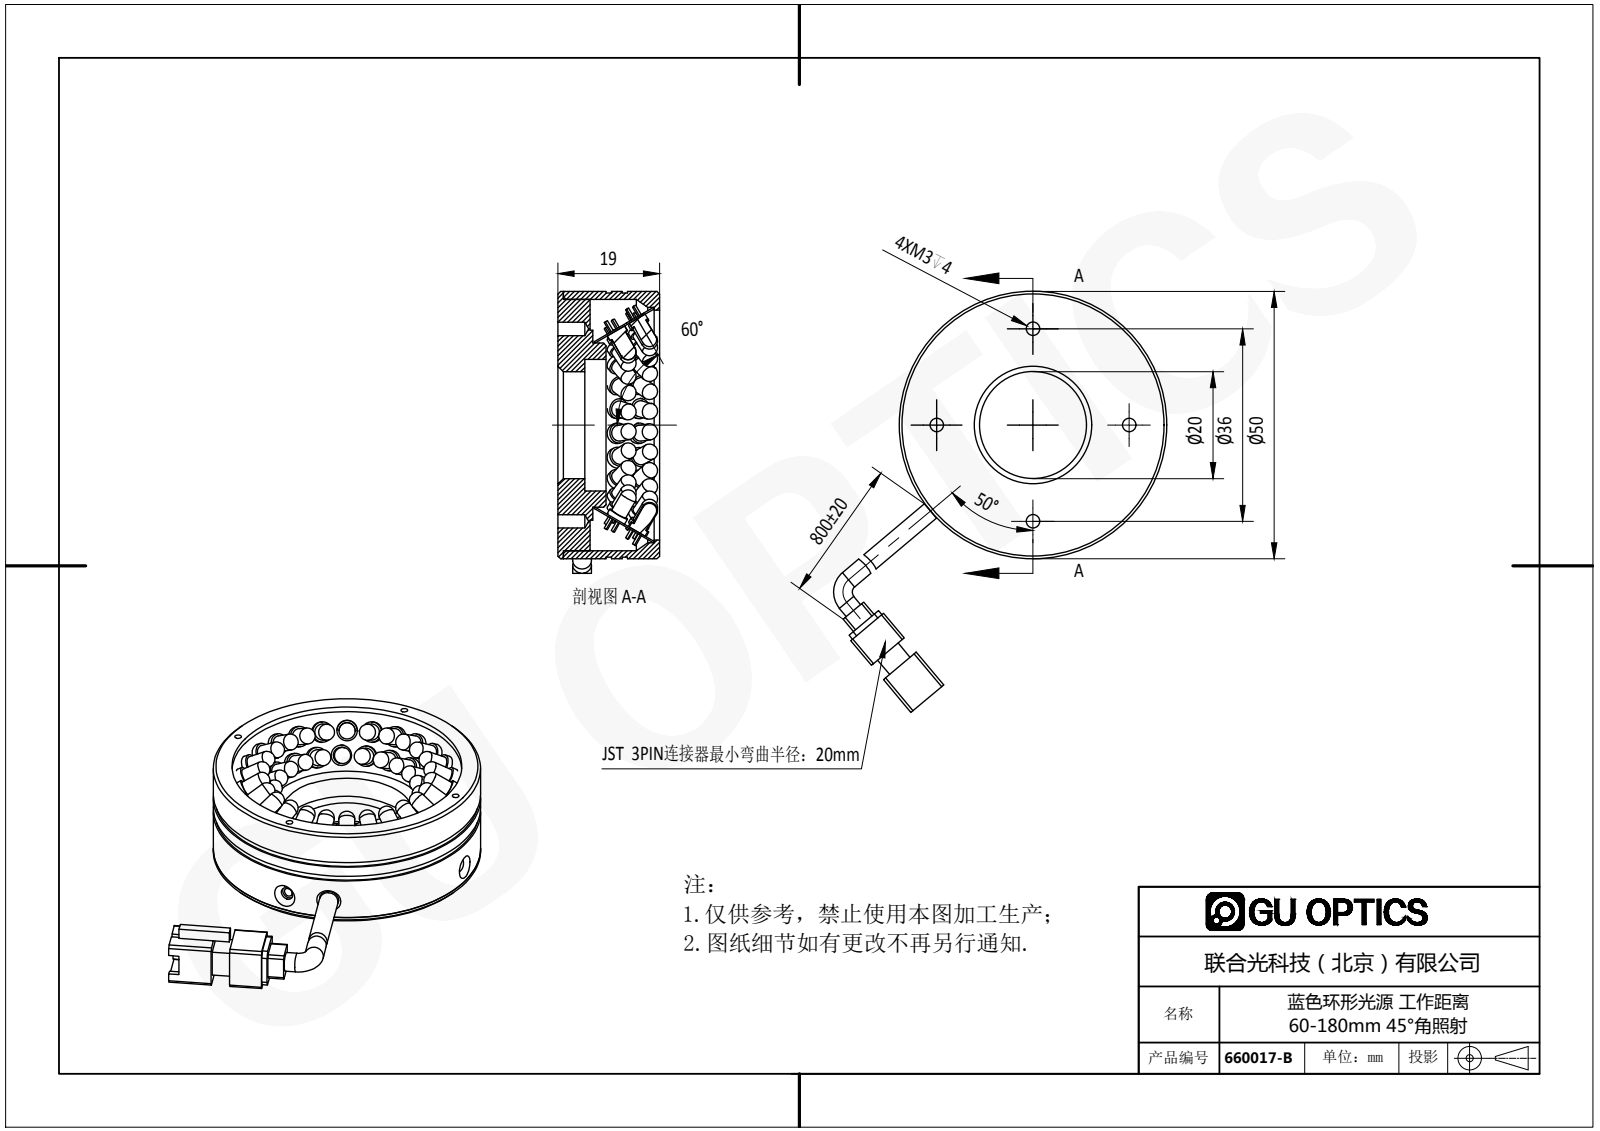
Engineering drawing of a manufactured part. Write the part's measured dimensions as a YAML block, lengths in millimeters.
part_name: "660017-B"
step_written_by: "SolidWorks 2016 (AUTOMOTIVE_DESIGN)"
units: millimeters
bodies: {solids: 54, faces: 1066, planar: 662, cylindrical: 300, other: 104}
overall_size: [82.93, 50, 19]
volume: 17639
surface_area: 20260
round_holes:
  - {diameter: 1.25, count: 4}
  - {diameter: 2.5, count: 4}
  - {diameter: 1.6, count: 2}
  - {diameter: 2.4, count: 2}
  - {diameter: 3, count: 2}
  - {diameter: 3.6, count: 1}
  - {diameter: 20, count: 1}
  - {diameter: 24.6, count: 1}
  - {diameter: 43, count: 1}
  - {diameter: 44, count: 1}
round_bosses_or_shafts:
  - {diameter: 3.8, count: 49}
  - {diameter: 3, count: 47}
  - {diameter: 3.5, count: 2}
  - {diameter: 50, count: 1}
  - {diameter: 49.4, count: 1}
  - {diameter: 47, count: 1}
  - {diameter: 35.54, count: 1}
  - {diameter: 30.72, count: 1}
partial_cylinders:
  - {radius: 0.5, count: 12}
  - {radius: 1, count: 4}
  - {radius: 4, count: 1}
face_to_face_distances: [1, 6, 0.5, 5, 5.5, 8, 3, 13, 2.5, 1.5]
hole_center_spacings: [11.66, 20.95, 23, 32.53, 18, 25.46, 35.6, 39.63]
